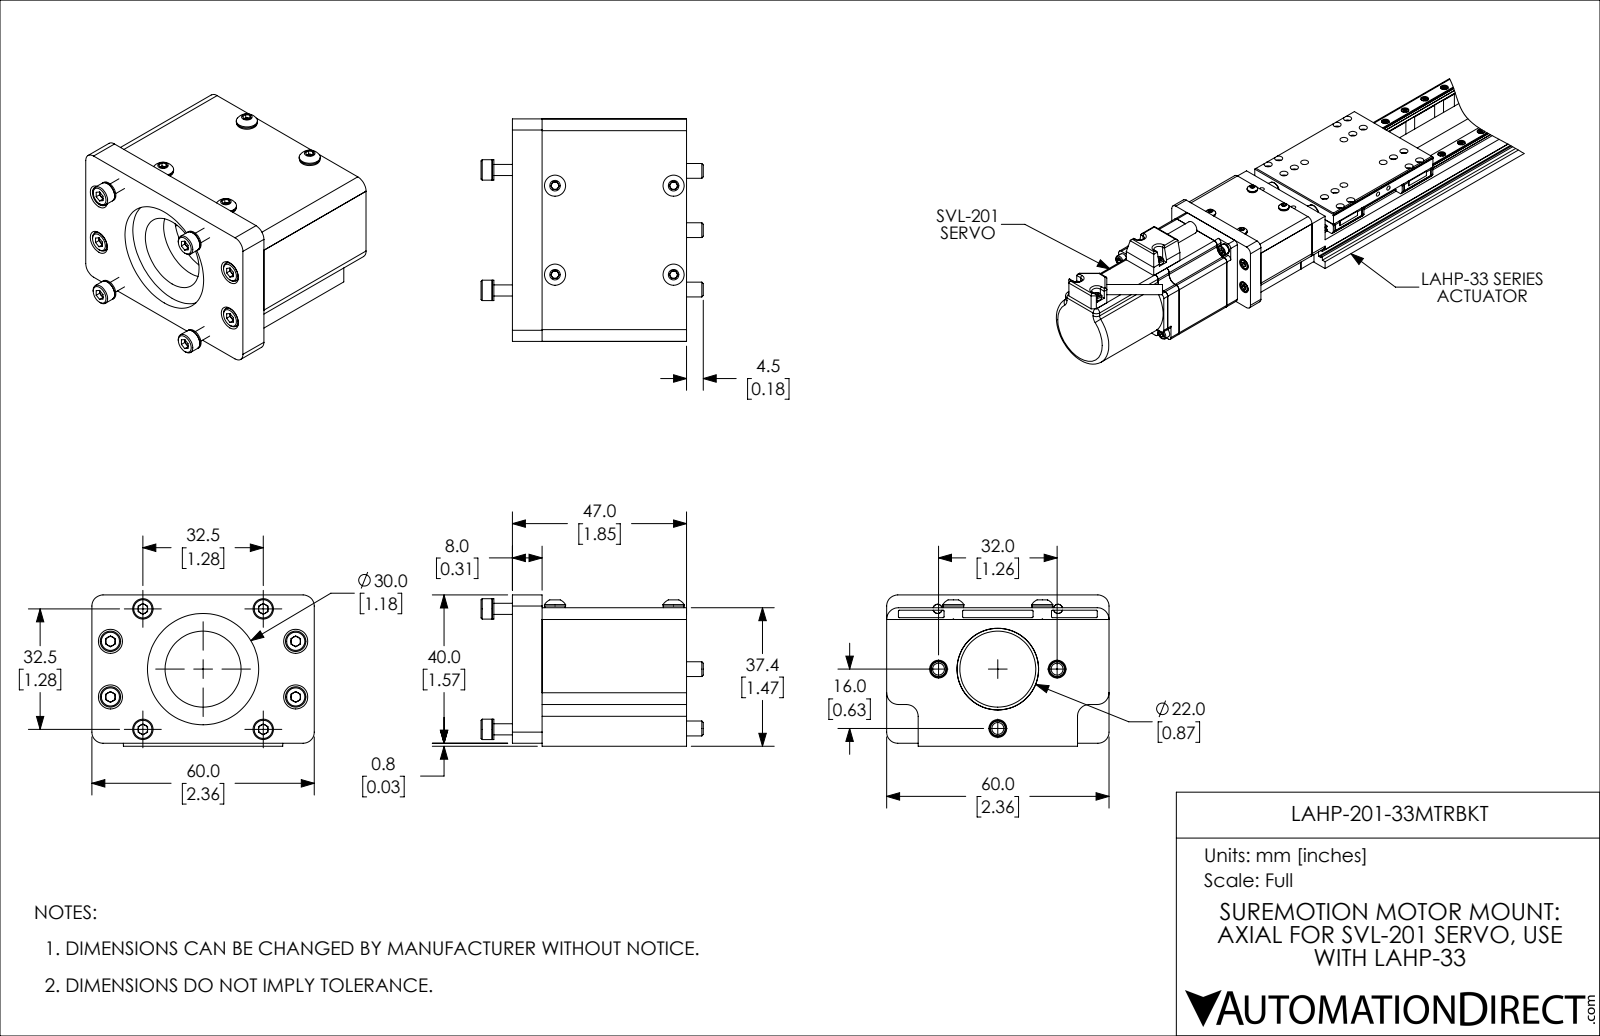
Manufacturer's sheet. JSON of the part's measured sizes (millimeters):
{"part_name": "LAHP-201-33MTRBKT", "step_written_by": "SolidWorks 2019 (CONFIG_CONTROL_DESIGN)", "units": "millimeters", "bodies": {"solids": 33, "faces": 679, "planar": 315, "cylindrical": 232, "other": 132}, "overall_size": [60, 59.9, 40.8], "volume_mm3": 59450, "surface_area_mm2": 35080, "round_holes": [[2.5, 16], [3.2, 12], [3.6, 8], [6.5, 4], [4.3, 3], [4.8, 3], [8, 3], [20.5, 1], [22, 1], [30, 1]], "round_bosses_or_shafts": [[5.5, 12], [3, 12], [5.7, 4], [7, 3], [4, 3], [22, 1]], "partial_cylinders_radius": [[0.3, 12], [3.2, 10], [3, 4]], "face_to_face_distances": [3.2, 0.5, 2, 2.5, 39, 34.2, 37.4, 34.7, 36.7, 2.7], "hole_center_spacings": [16.3, 36.1, 6.4, 10.1, 10.3, 11.7, 12.4, 18]}
